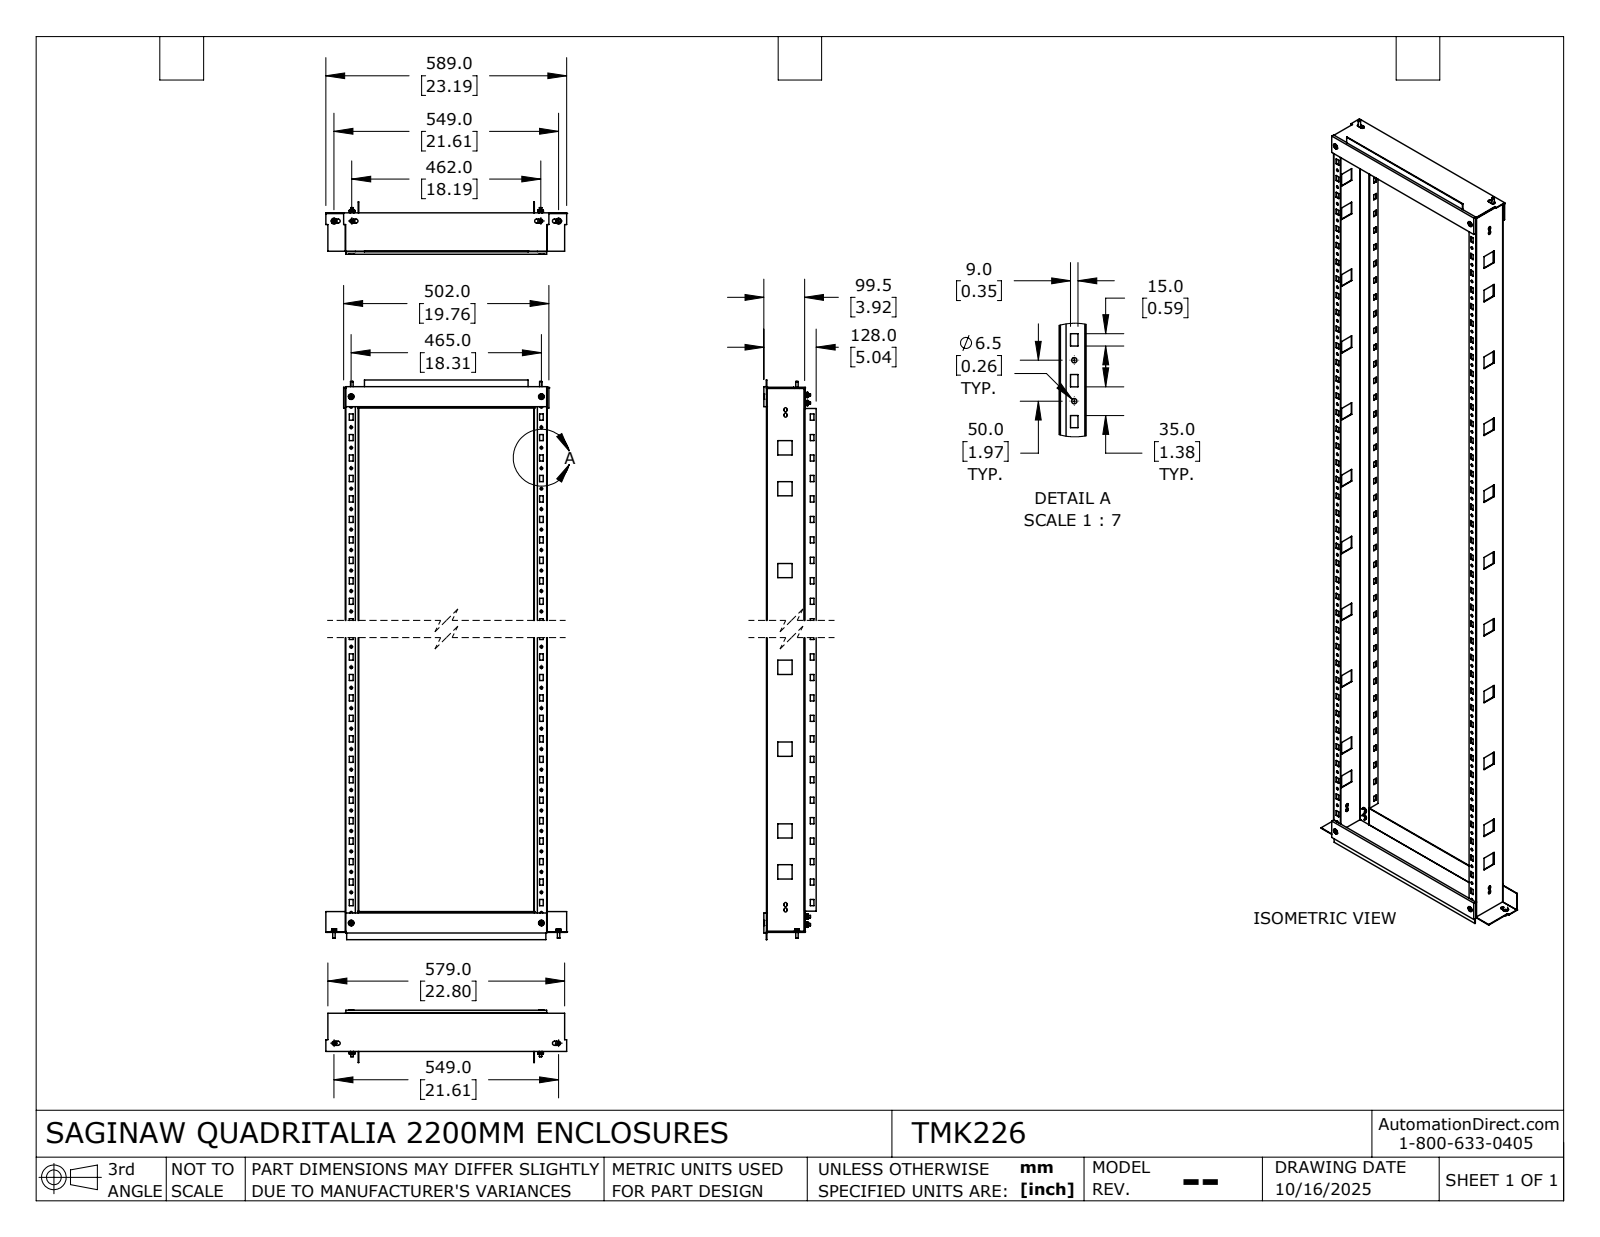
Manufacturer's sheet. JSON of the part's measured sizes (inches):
{"part_name": "TMK226", "step_written_by": "SolidWorks 2024 (AUTOMOTIVE_DESIGN)", "units": "inches", "bodies": {"solids": 1, "faces": 2474, "planar": 1688, "cylindrical": 646, "other": 140}, "overall_size": [83.917, 23.189, 5.051], "volume_in3": 83.9, "surface_area_in2": 2868, "round_holes": [[0.256, 82], [0.276, 8], [0.156, 4]], "round_bosses_or_shafts": [[0.236, 16], [0.551, 12], [0.472, 4], [0.394, 4]], "partial_cylinders_radius": [[0.01, 96], [0.02, 80], [0.039, 32], [0.138, 24], [0.177, 16], [0.197, 8], [0.059, 6]], "face_to_face_distances": [0.059, 19.39, 1.24, 18.15, 19.331, 19.449, 3.602, 3.661, 1.181, 18.091], "hole_center_spacings": [3.937, 7.874, 11.811, 15.748, 1.969, 19.685, 5.906, 9.843]}
